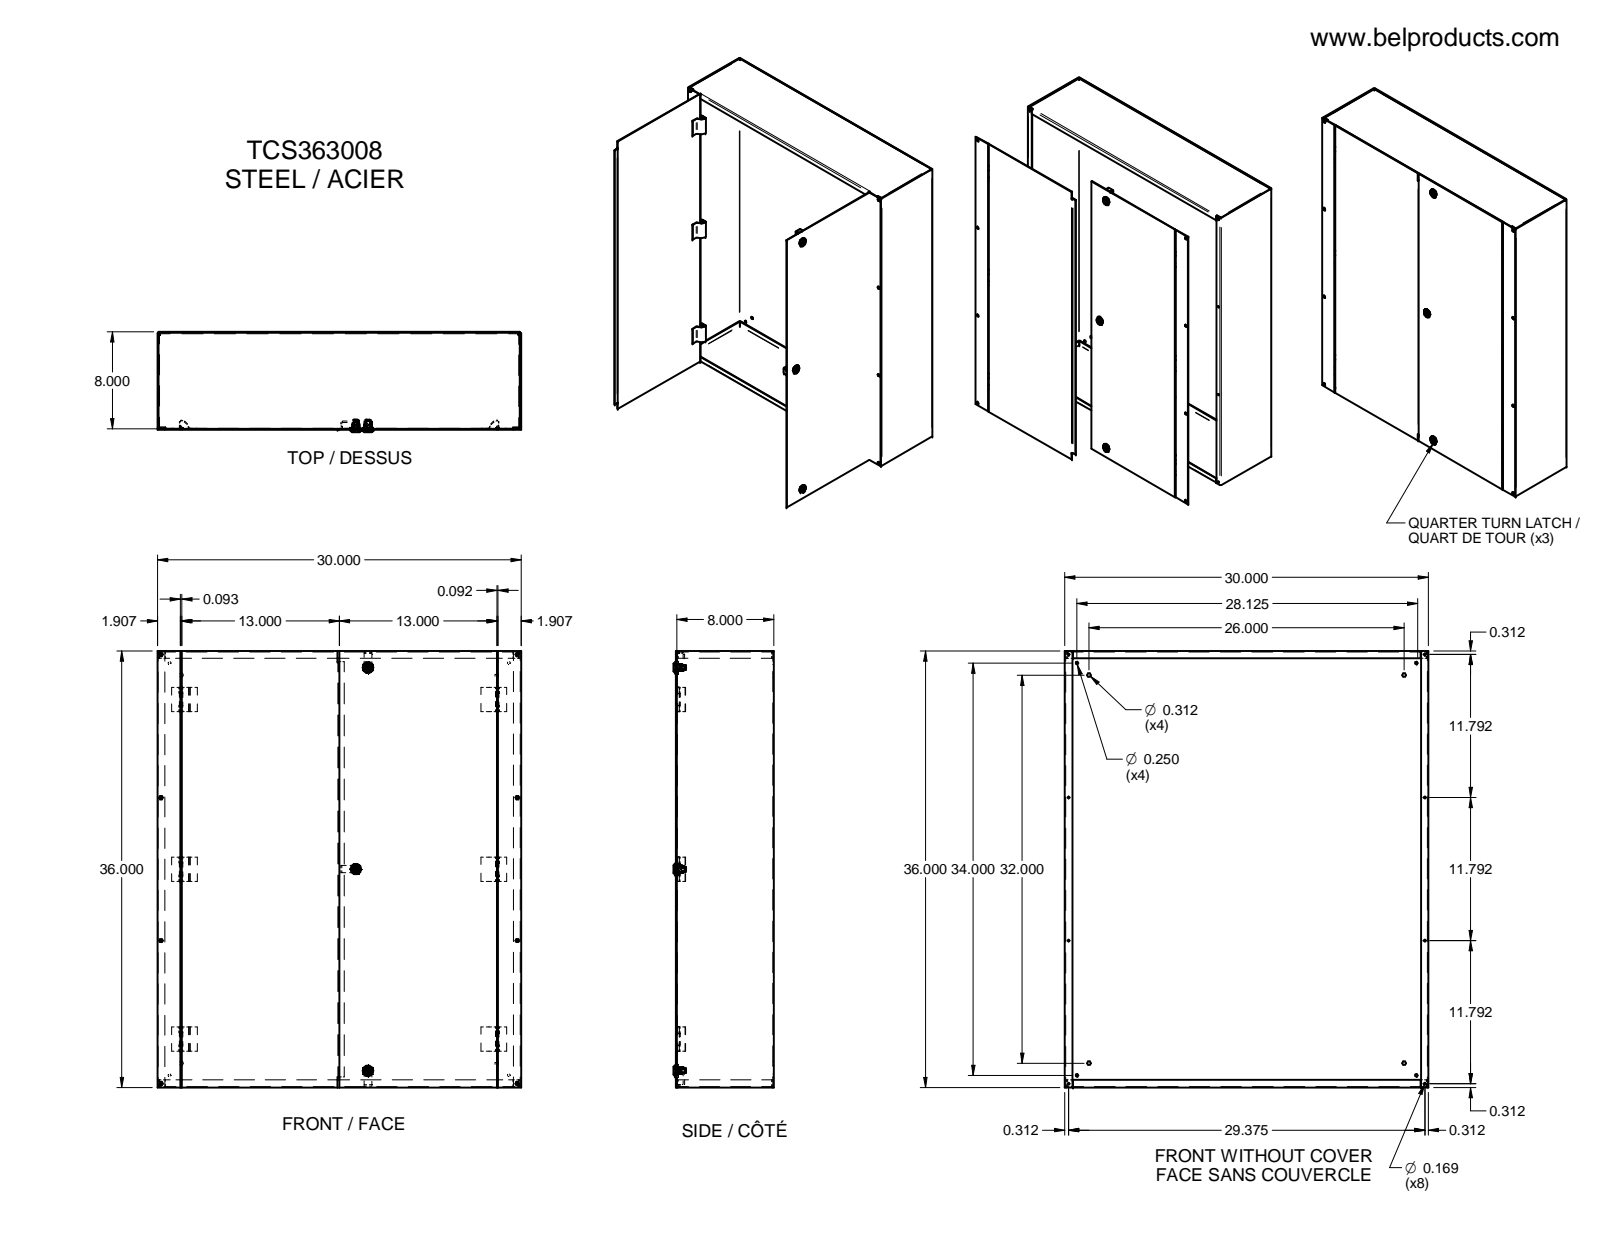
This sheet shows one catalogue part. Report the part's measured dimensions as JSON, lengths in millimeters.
{"part_name": "LOCK AVEC TOURNEVIS TYPE 4-12 SANS CAME; HOSING-oa0; INSERT POUR TOURNEVIS-oa1; NOIX DE FIXATION-oa2 (+8 more)", "step_written_by": "Unknown (AUTOMOTIVE_DESIGN)", "units": "millimeters", "bodies": {"solids": 46, "faces": 1693, "planar": 850, "cylindrical": 421, "other": 422}, "overall_size": [914.4, 762, 209.57], "volume_mm3": 4150000, "surface_area_mm2": 4406000, "round_holes": [[7.92, 12], [4.29, 8], [6.35, 4], [9.1, 3], [11.18, 3], [12.83, 3], [15.8, 3], [17.46, 3], [3.81, 2], [6.99, 2]], "round_bosses_or_shafts": [[22.86, 3], [22.61, 3], [15.75, 3], [12.95, 3], [12.62, 3], [12.19, 3], [11.86, 3], [10.08, 3]], "partial_cylinders_radius": [[9.53, 34], [0.25, 24], [0.81, 17], [2.72, 14], [9.42, 6], [1.52, 4], [3.05, 4], [3.48, 3]], "face_to_face_distances": [1.91, 203.2, 1.9, 201.29, 205.11, 760.1, 912.5, 762, 758.2, 914.4], "hole_center_spacings": [803.99, 24.69, 35.92, 60.61, 260.2, 282.59, 299.51, 557.8]}
